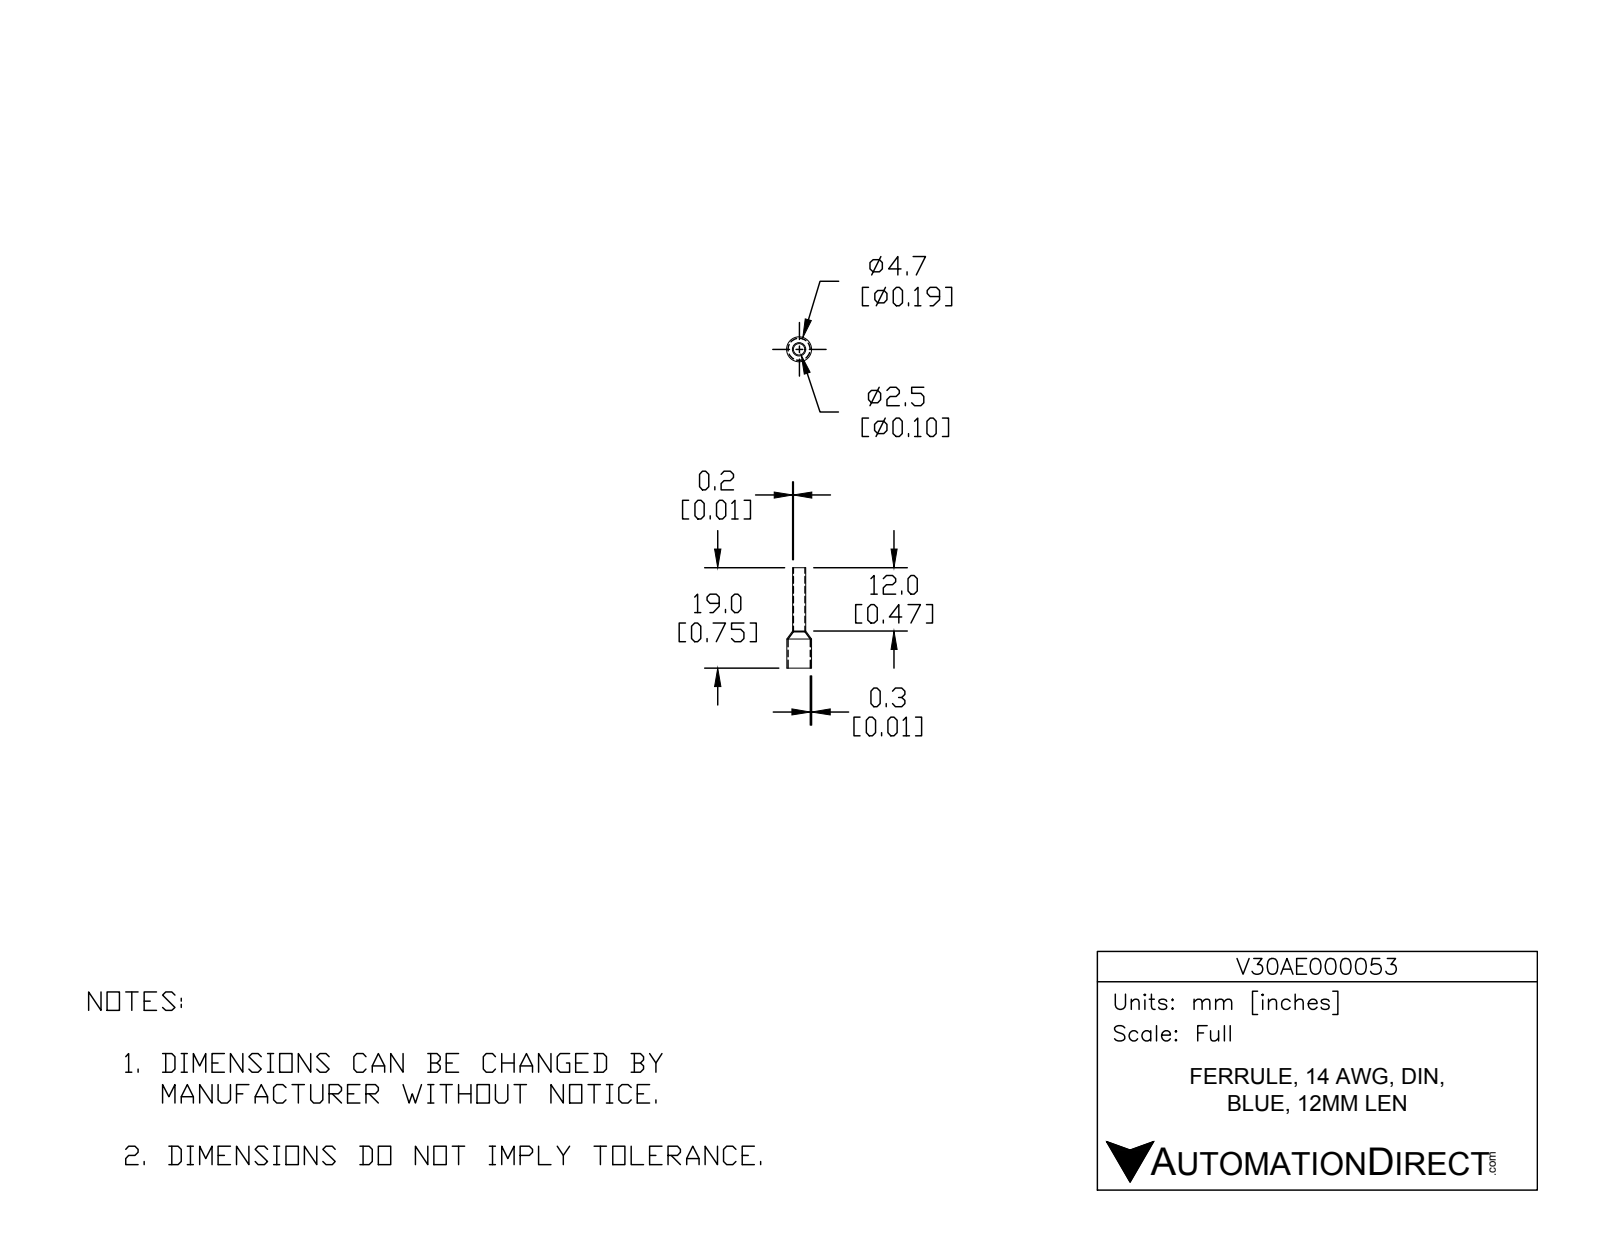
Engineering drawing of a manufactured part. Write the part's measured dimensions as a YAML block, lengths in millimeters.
part_name: "V30AE000053"
step_written_by: "SolidWorks 2017 (AUTOMOTIVE_DESIGN)"
units: millimeters
bodies: {solids: 1, faces: 14, planar: 2, cylindrical: 8, other: 4}
overall_size: [19, 4.7, 4.7]
volume: 36
surface_area: 375
round_holes:
  - {diameter: 2.2, count: 1}
  - {diameter: 4.2, count: 1}
round_bosses_or_shafts:
  - {diameter: 4.7, count: 1}
  - {diameter: 2.5, count: 1}
face_to_face_distances: [19]
